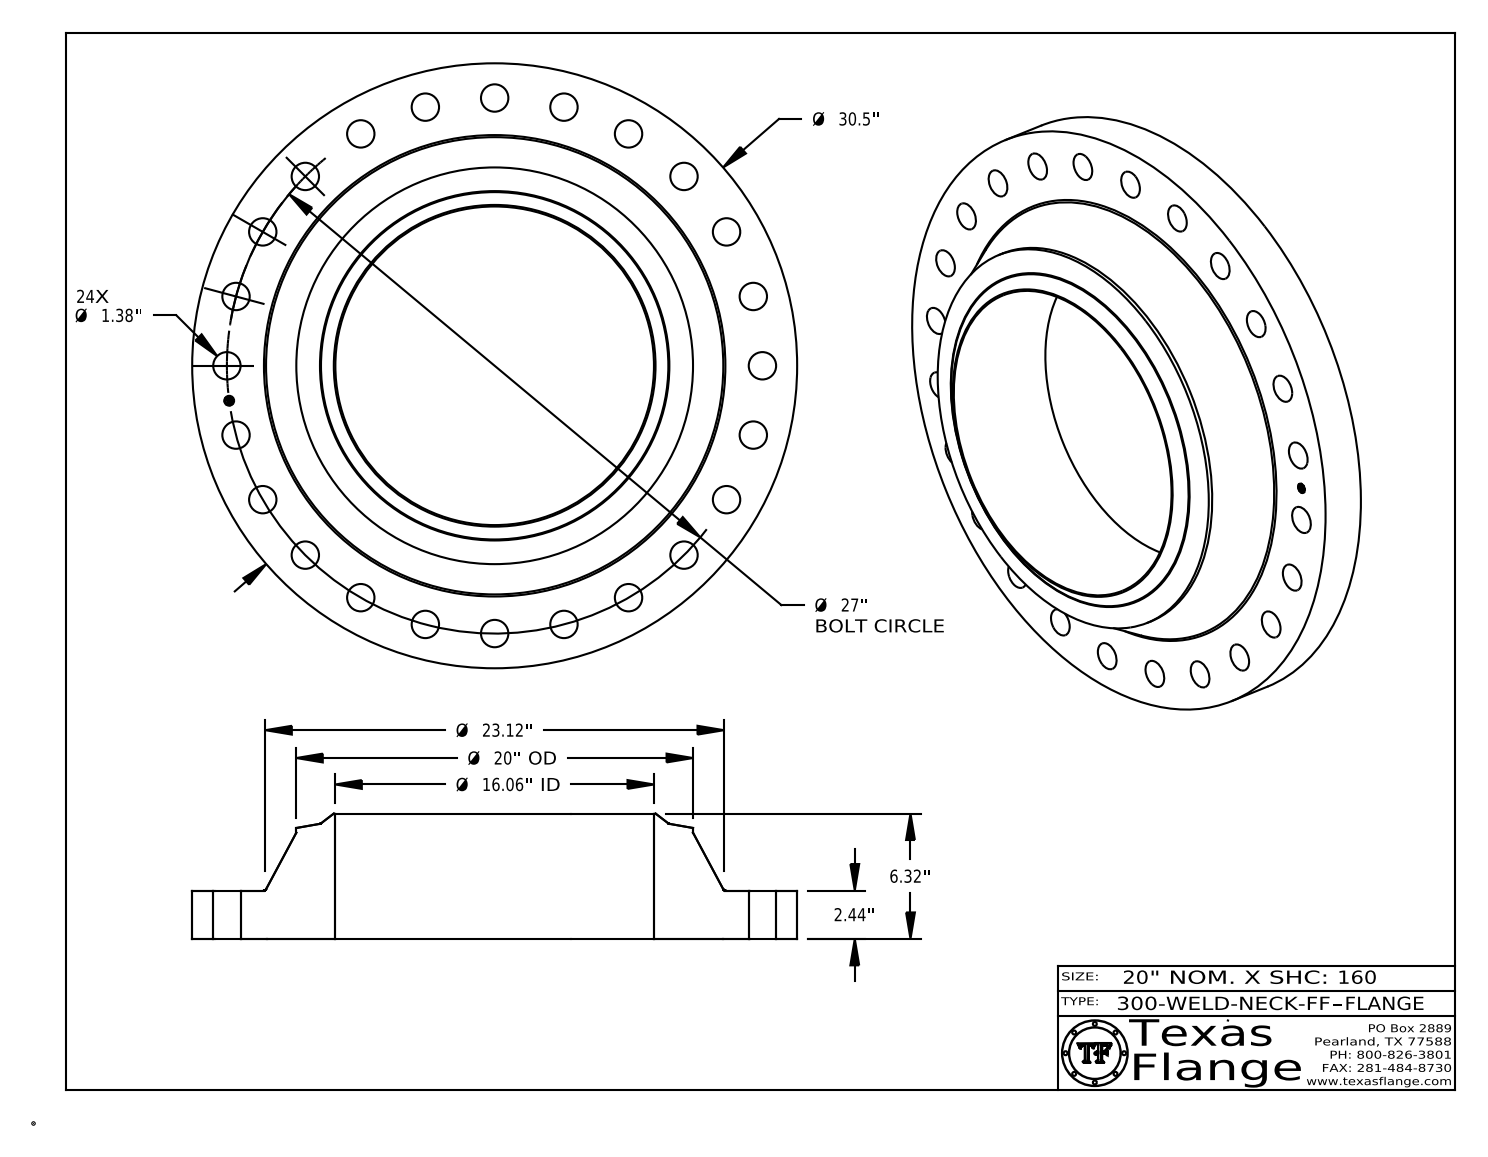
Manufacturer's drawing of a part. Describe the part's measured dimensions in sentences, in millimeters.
The part is named "300-WELD-NECK-FF". Its 3-D file was written by "CATIA V5 STEP AP214 (AUTOMOTIVE_DESIGN)". It is 1 solid with 453 faces: 369 planar, 74 cylindrical and 10 other. Overall it measures 774.7 by 774.7 by 160.5 millimeters. Its volume is 28 350 000 cubic millimeters and its surface area 1 247 000 square millimeters. Round holes: 24 of diameter 35.1, 1 of diameter 12.6, 1 of diameter 408. Round bosses or shafts: 8 of diameter 0.8, 1 of diameter 774.7, 1 of diameter 508, 1 of diameter 9.9. The main face-to-face distances are 62, 160.5, 98.6, 61.6, 0.4, 98.9, 3.8, 3.7, 0.7, 2.4. The hole center spacings are 342.9, 89.5, 177.5, 262.5, 417.5, 633.6, 679.9, 544.1.
